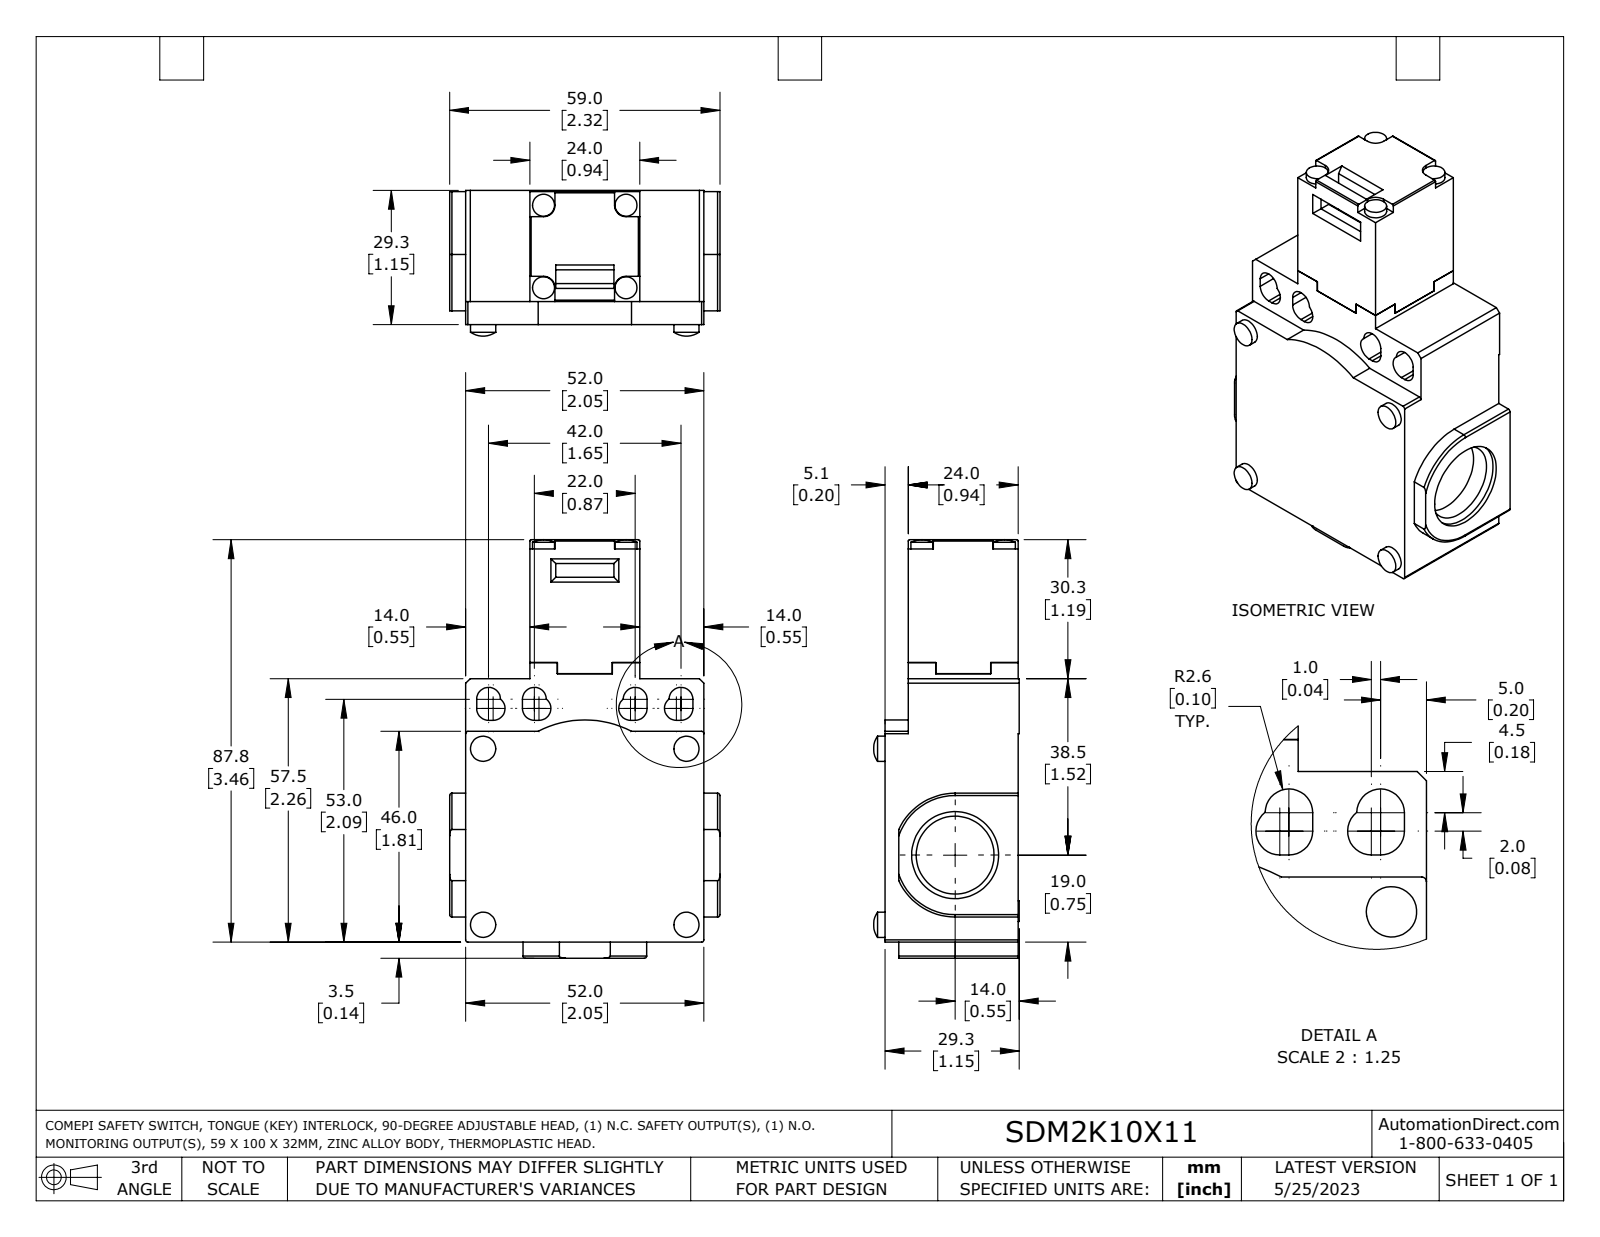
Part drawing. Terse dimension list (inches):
name: SDM2K10X11
written by: SolidWorks 2021 (AUTOMOTIVE_DESIGN)
unit: in
bodies: 2 solids, 181 faces (105 planar, 59 cylindrical, 17 other)
size: 3.594 × 2.323 × 1.252
volume: 6.047 in³; area: 33.47 in²
holes: 2× ⌀0.669, 2× ⌀0.748
bosses: 4× ⌀0.217, 4× ⌀0.189
rounds: 12× R0.102, 10× R0.02, 4× R0.012, 4× R0.098, 2× R0.531, 1× R0.394, 1× R0.4, 1× R0.866
face distances: 1.144, 0.945, 0.551, 1.496, 0.138, 0.199, 2.047, 2.307, 0.236, 2.185
